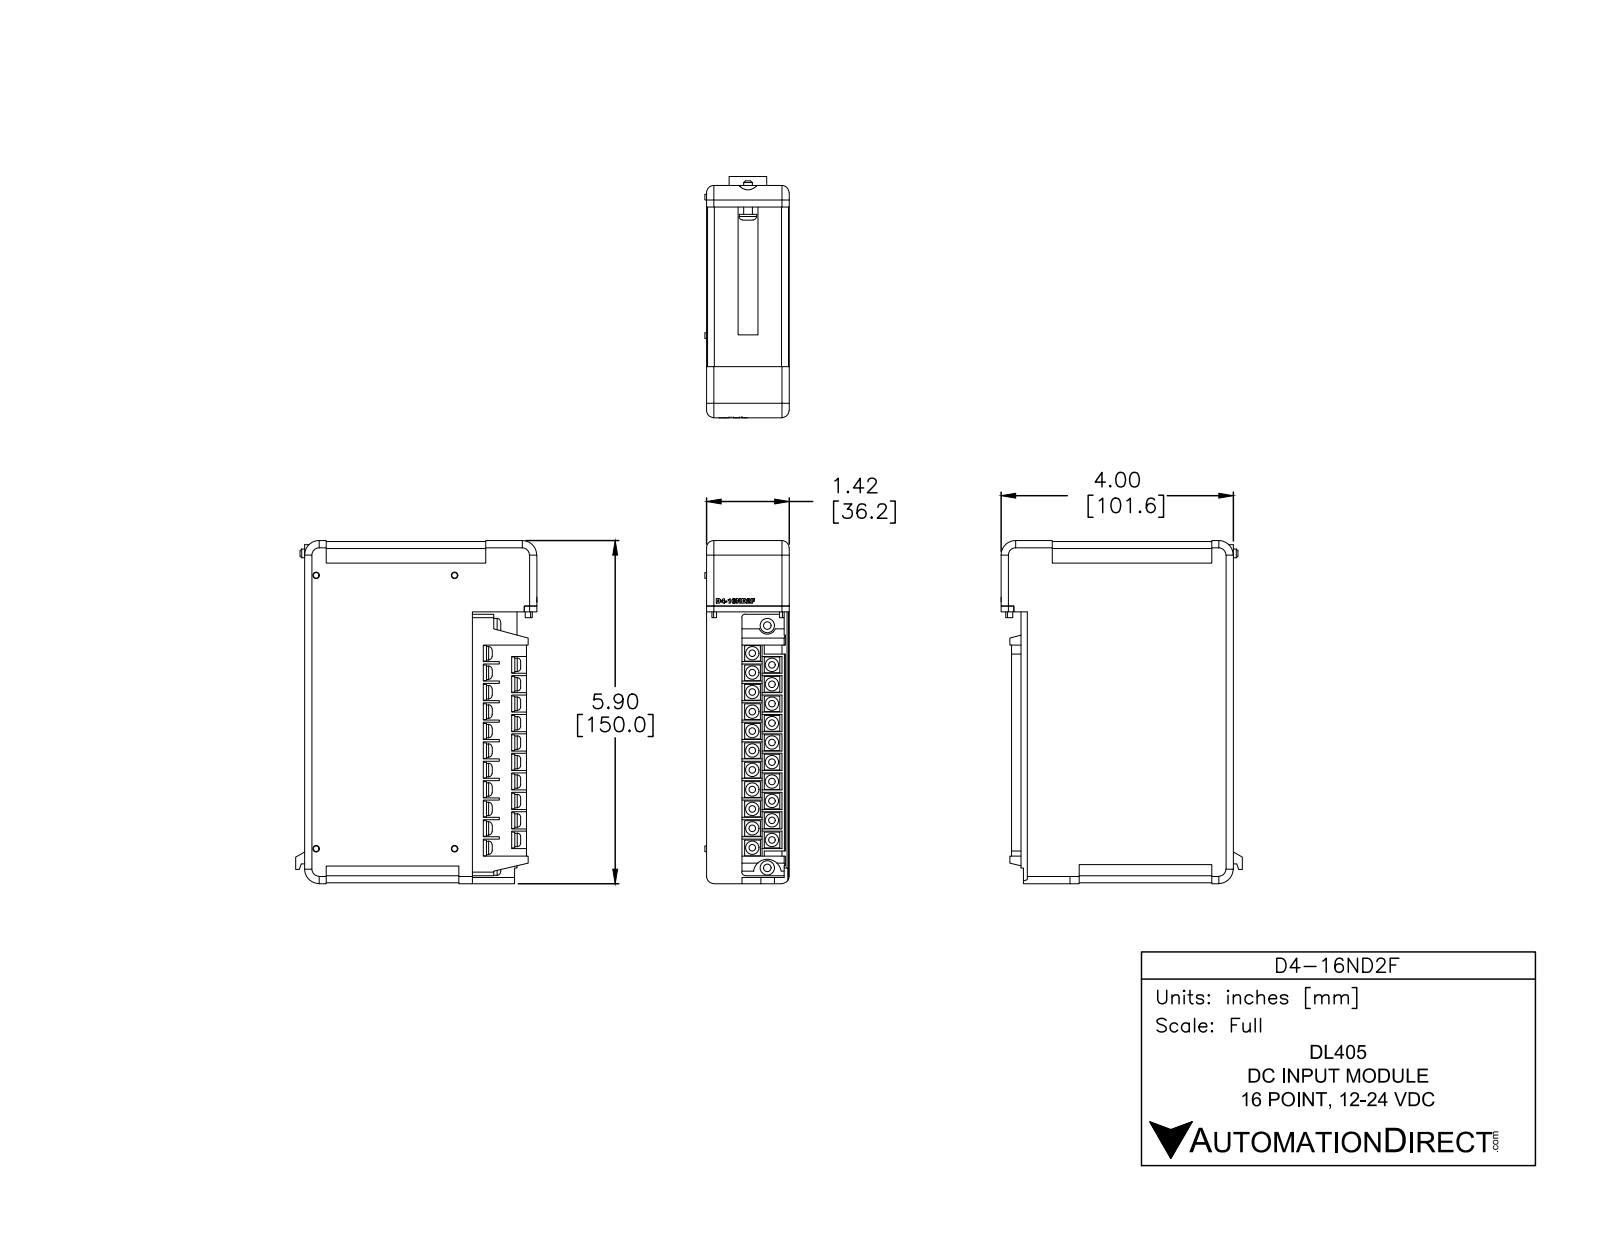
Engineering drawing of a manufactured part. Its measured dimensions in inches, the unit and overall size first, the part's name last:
Units: inches
Overall size (bounding box): 5.905 × 4.156 × 1.455
Round bosses / shafts (diameter × count): ⌀0.23 ×21, ⌀0.25 ×2, ⌀0.3 ×1, ⌀0.15 ×1
Partial cylindrical surfaces — rounded edges, fillets, slot ends (radius × count): R0.125 ×8, R0.12 ×4, R0.25 ×3, R0.015 ×2, R0.03 ×2, R0.06 ×2, R0.149 ×1, R0.151 ×1
Main face-to-face distances: 1.425, 0.015, 2.89, 5.875, 1.41, 0.47, 0.2, 0.955, 5.89, 1.21
Volume: 27.51 in³ · Surface area: 86.83 in²
Bodies: 15 solids, 617 faces (426 planar, 86 cylindrical, 105 other)
Part name (STEP PRODUCT): D4-16ND2F
STEP written by: SolidWorks 2014 (AUTOMOTIVE_DESIGN)
